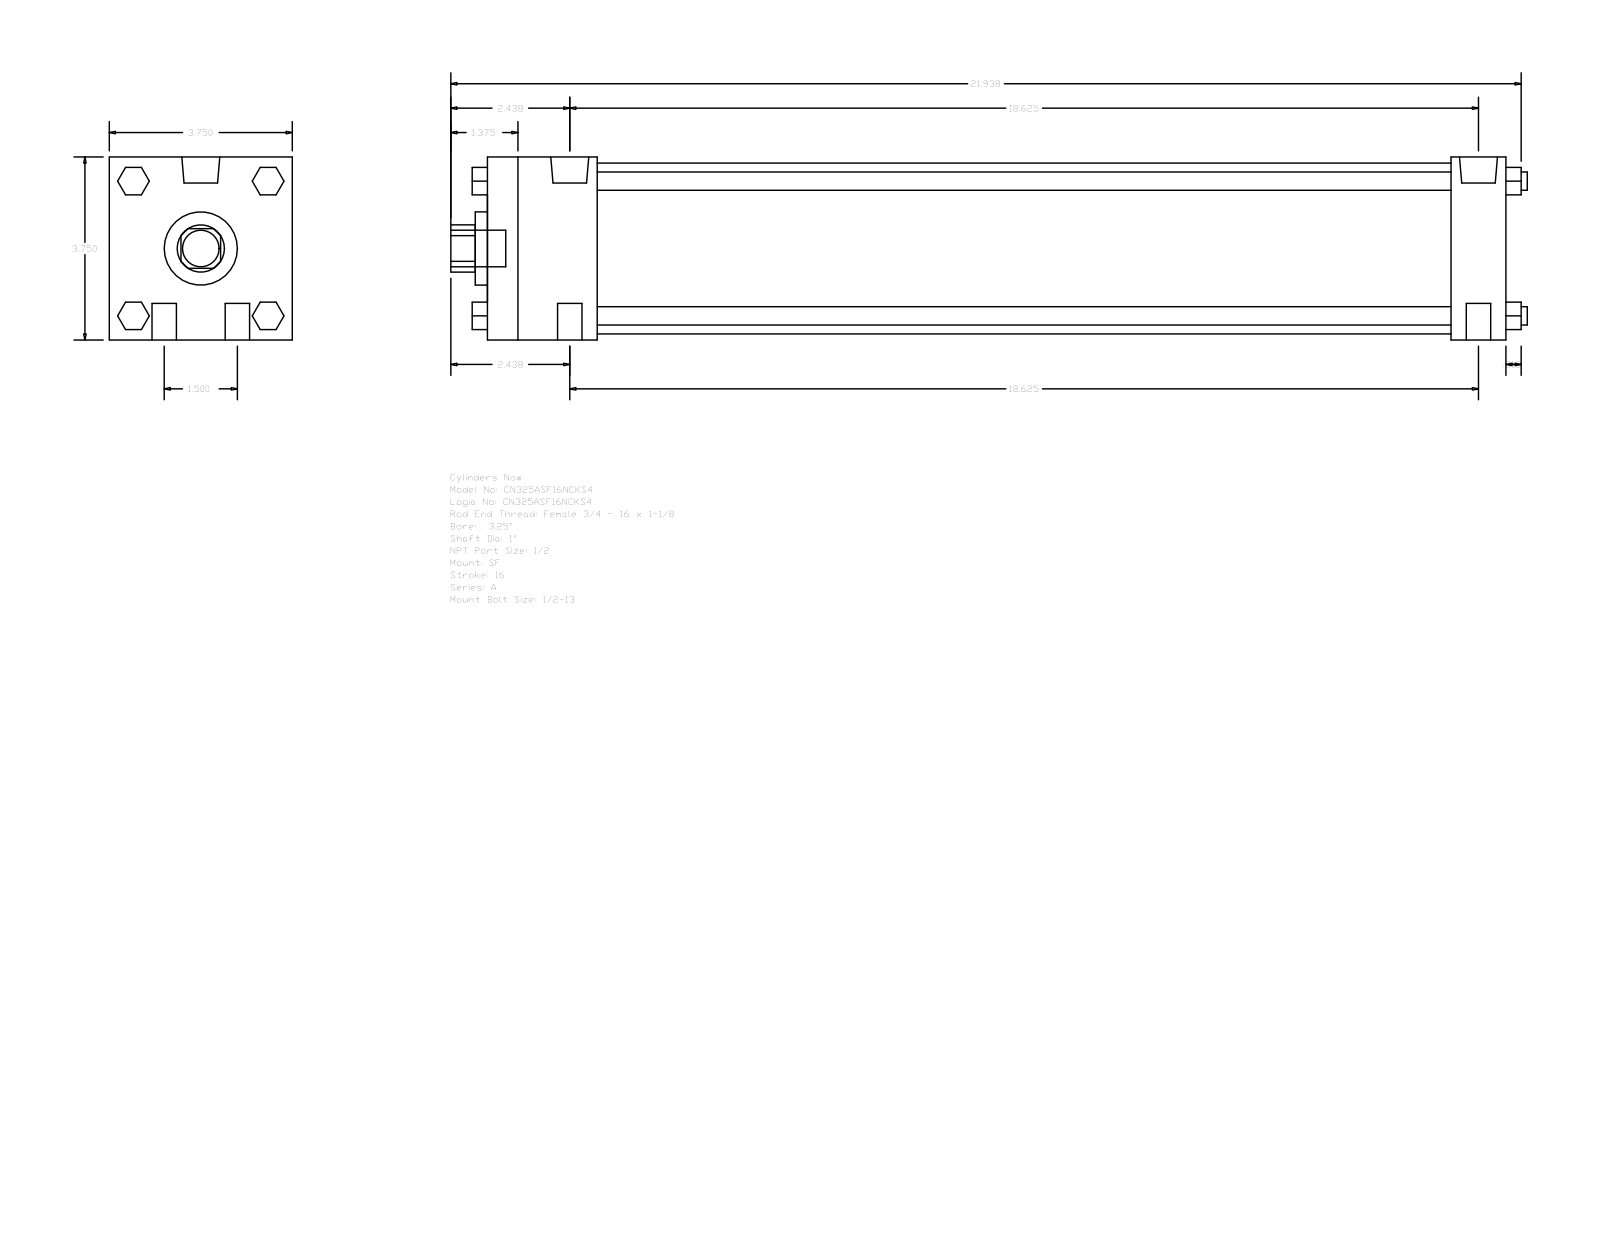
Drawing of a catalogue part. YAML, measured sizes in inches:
part_name: "A_SF__0325_1"
step_written_by: "GSSL Pune (CONFIG_CONTROL_DESIGN)"
units: inches
bodies: {solids: 0, faces: 124, planar: 94, cylindrical: 30, other: 0}
overall_size: [22.063, 3.75, 3.75]
round_holes:
  - {diameter: 1, count: 1}
  - {diameter: 1.5, count: 1}
  - {diameter: 3.5, count: 1}
round_bosses_or_shafts:
  - {diameter: 0.5, count: 4}
  - {diameter: 0.375, count: 4}
  - {diameter: 0.778, count: 2}
  - {diameter: 0.344, count: 2}
  - {diameter: 0.75, count: 1}
partial_cylinders:
  - {radius: 0.484, count: 1}
face_to_face_distances: [3.75, 20.875, 1.125, 19.75, 2.25, 17.5, 18.625, 0.562, 1.38, 2.39]
